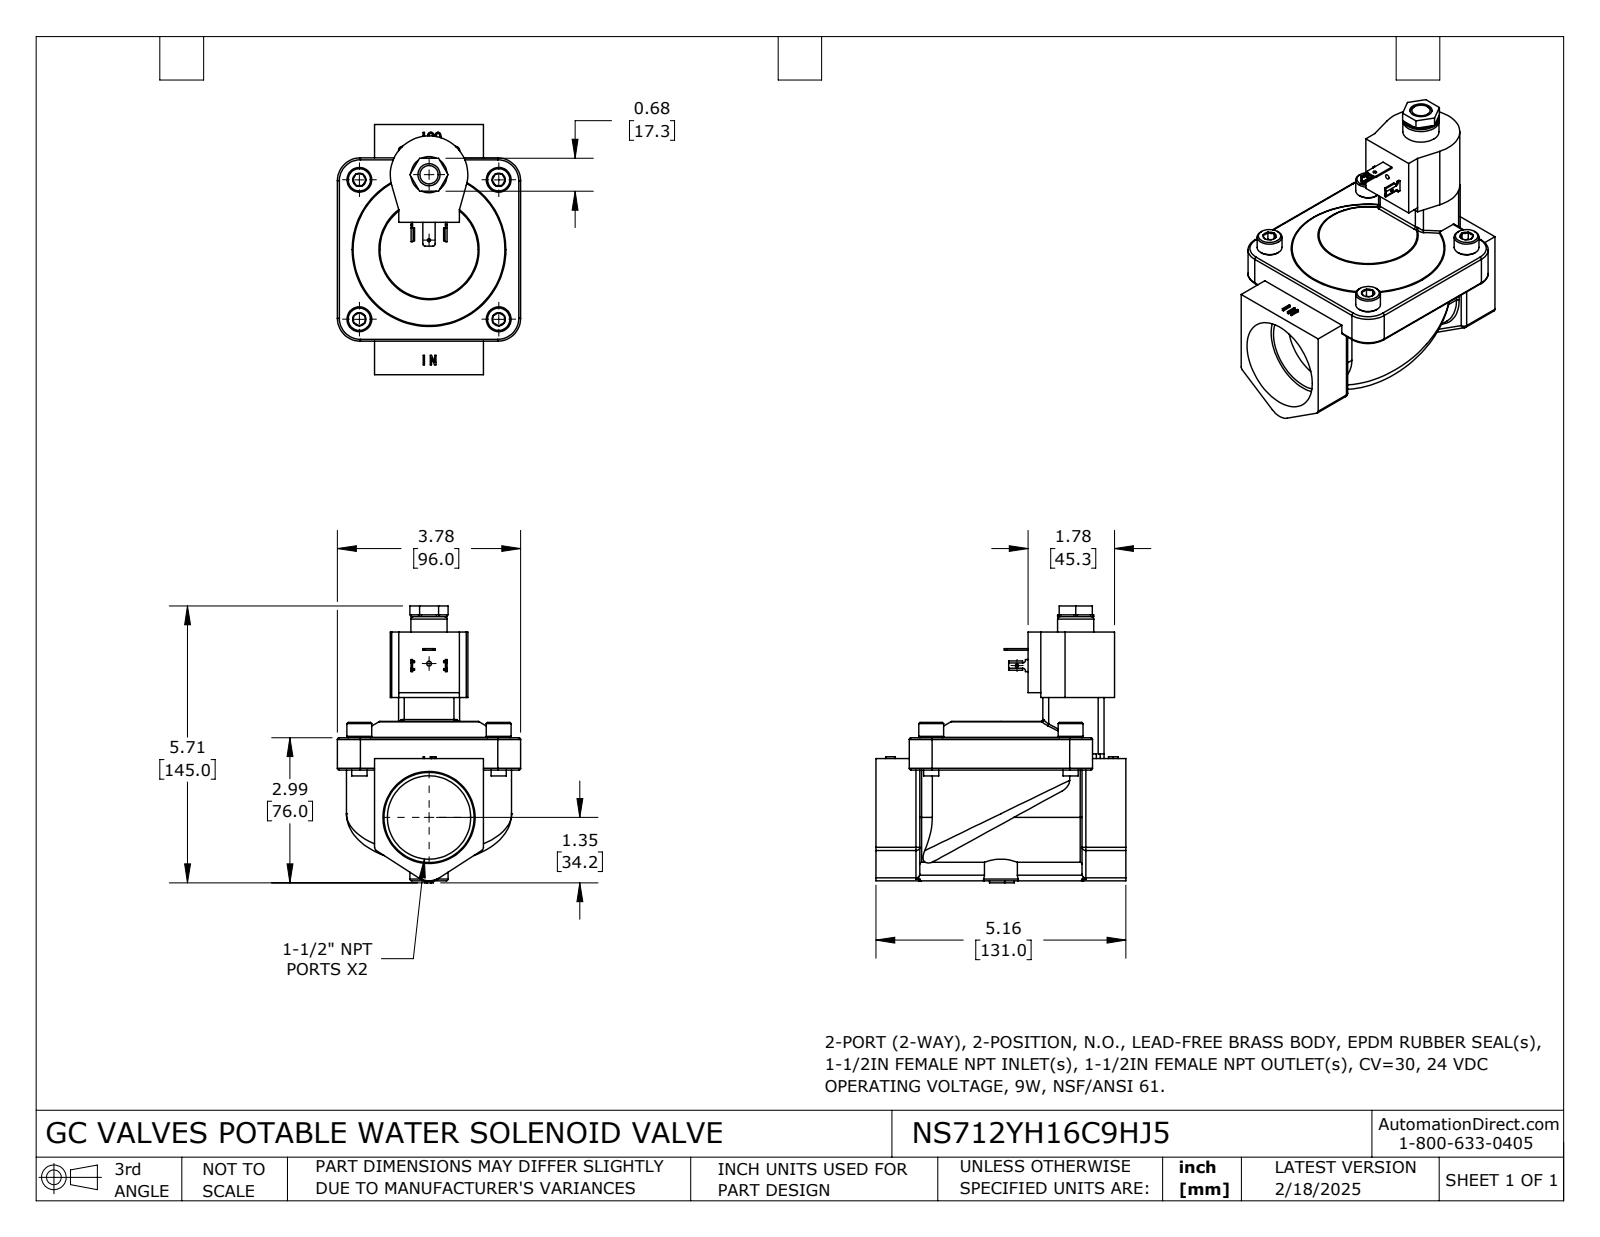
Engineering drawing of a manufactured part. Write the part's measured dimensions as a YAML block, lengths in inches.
part_name: "NS712YH16C9HJ5"
step_written_by: "SolidWorks 2024 (CONFIG_CONTROL_DESIGN)"
units: inches
bodies: {solids: 1, faces: 456, planar: 206, cylindrical: 120, other: 130}
overall_size: [5.709, 5.157, 3.78]
volume: 33.03
surface_area: 111.5
round_holes:
  - {diameter: 0.066, count: 1}
  - {diameter: 0.067, count: 1}
  - {diameter: 0.1, count: 1}
  - {diameter: 0.456, count: 1}
  - {diameter: 1.2, count: 1}
  - {diameter: 1.719, count: 1}
round_bosses_or_shafts:
  - {diameter: 0.512, count: 4}
  - {diameter: 0.315, count: 4}
  - {diameter: 0.746, count: 1}
partial_cylinders:
  - {radius: 0.079, count: 14}
  - {radius: 0.039, count: 13}
  - {radius: 0.118, count: 6}
  - {radius: 0.006, count: 4}
  - {radius: 0.041, count: 4}
  - {radius: 0.472, count: 4}
  - {radius: 0.008, count: 2}
  - {radius: 0.05, count: 2}
face_to_face_distances: [0.768, 0.433, 1.26, 0.236, 3.012, 0.335, 3.78, 0.669, 1.004, 2.244]
hole_center_spacings: [1.35, 3.172]
